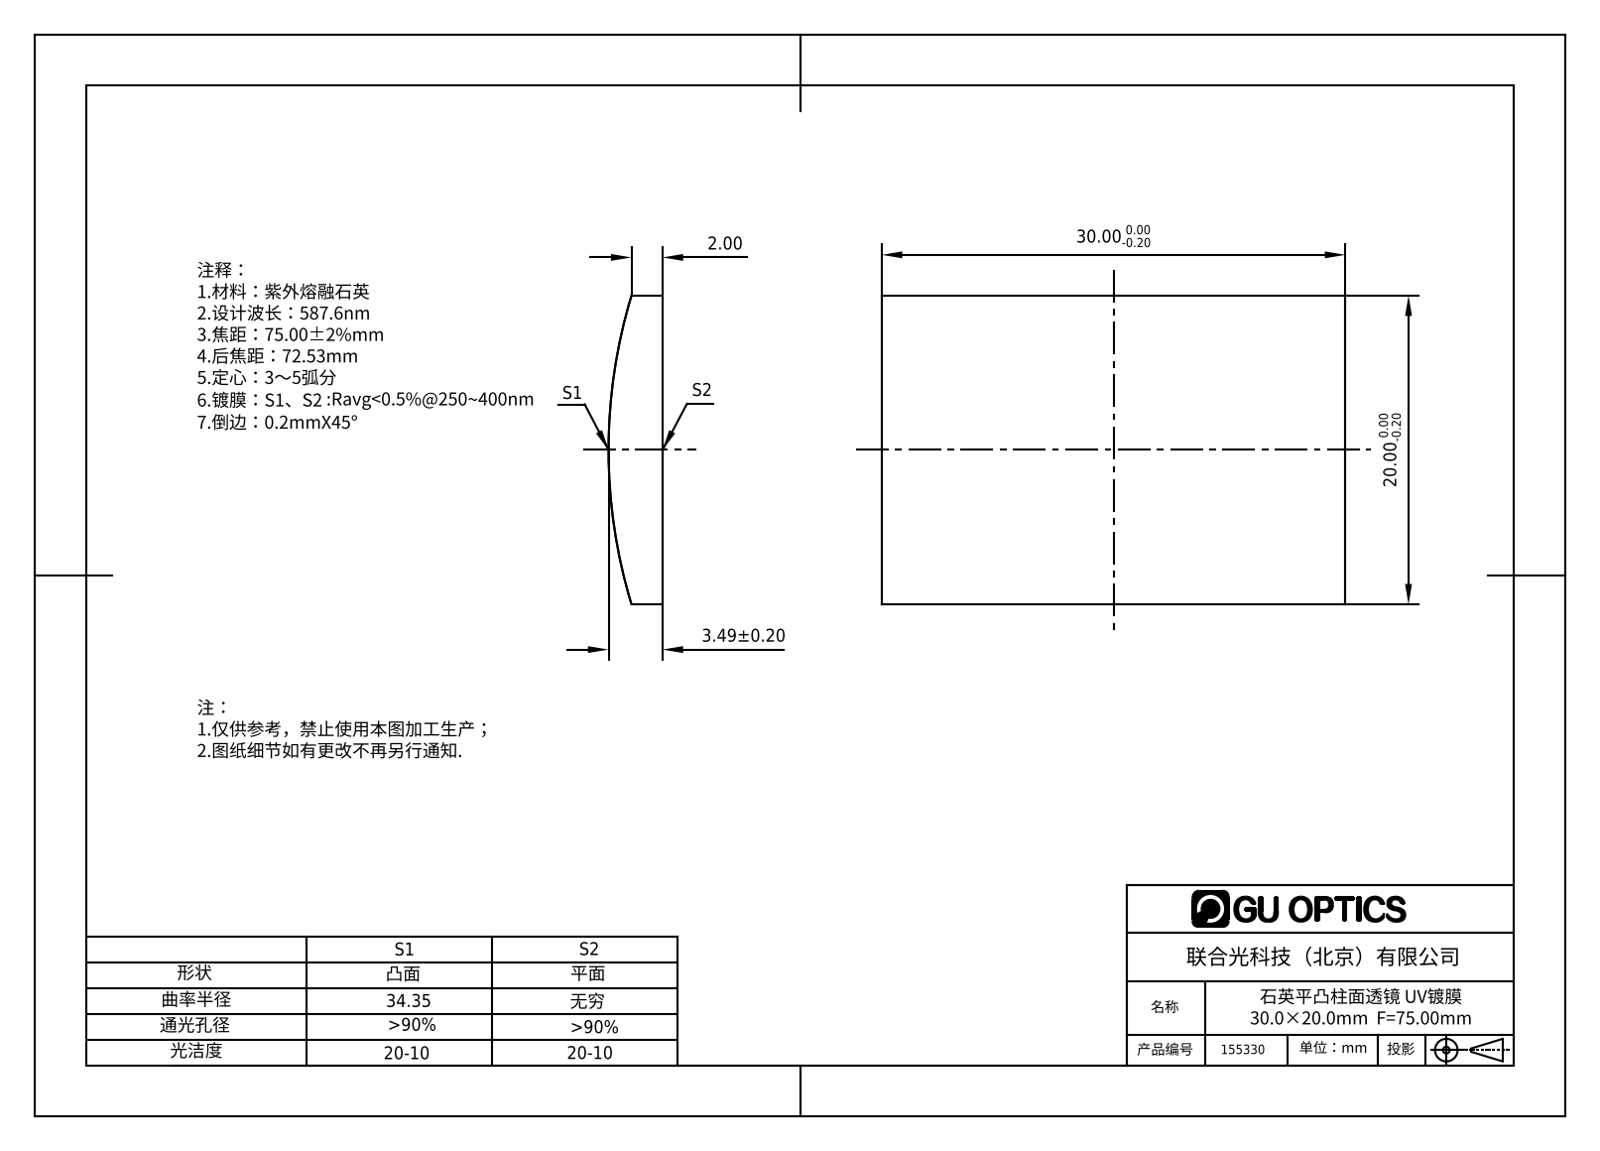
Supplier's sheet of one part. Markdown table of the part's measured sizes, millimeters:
| quantity | value |
| --- | --- |
| part name | 155296 |
| STEP written by | SolidWorks 2016 (AUTOMOTIVE_DESIGN) |
| units | millimeters |
| bodies | 1 solid, 6 faces (5 planar, 1 cylindrical, 0 other) |
| overall size | 30 × 20 × 3.49 |
| volume | 1 799 mm³ |
| surface area | 1 449 mm² |
| partial cylindrical surfaces (radius × count) | 34.35 × 1 |
| main face-to-face distances | 20, 30 |
